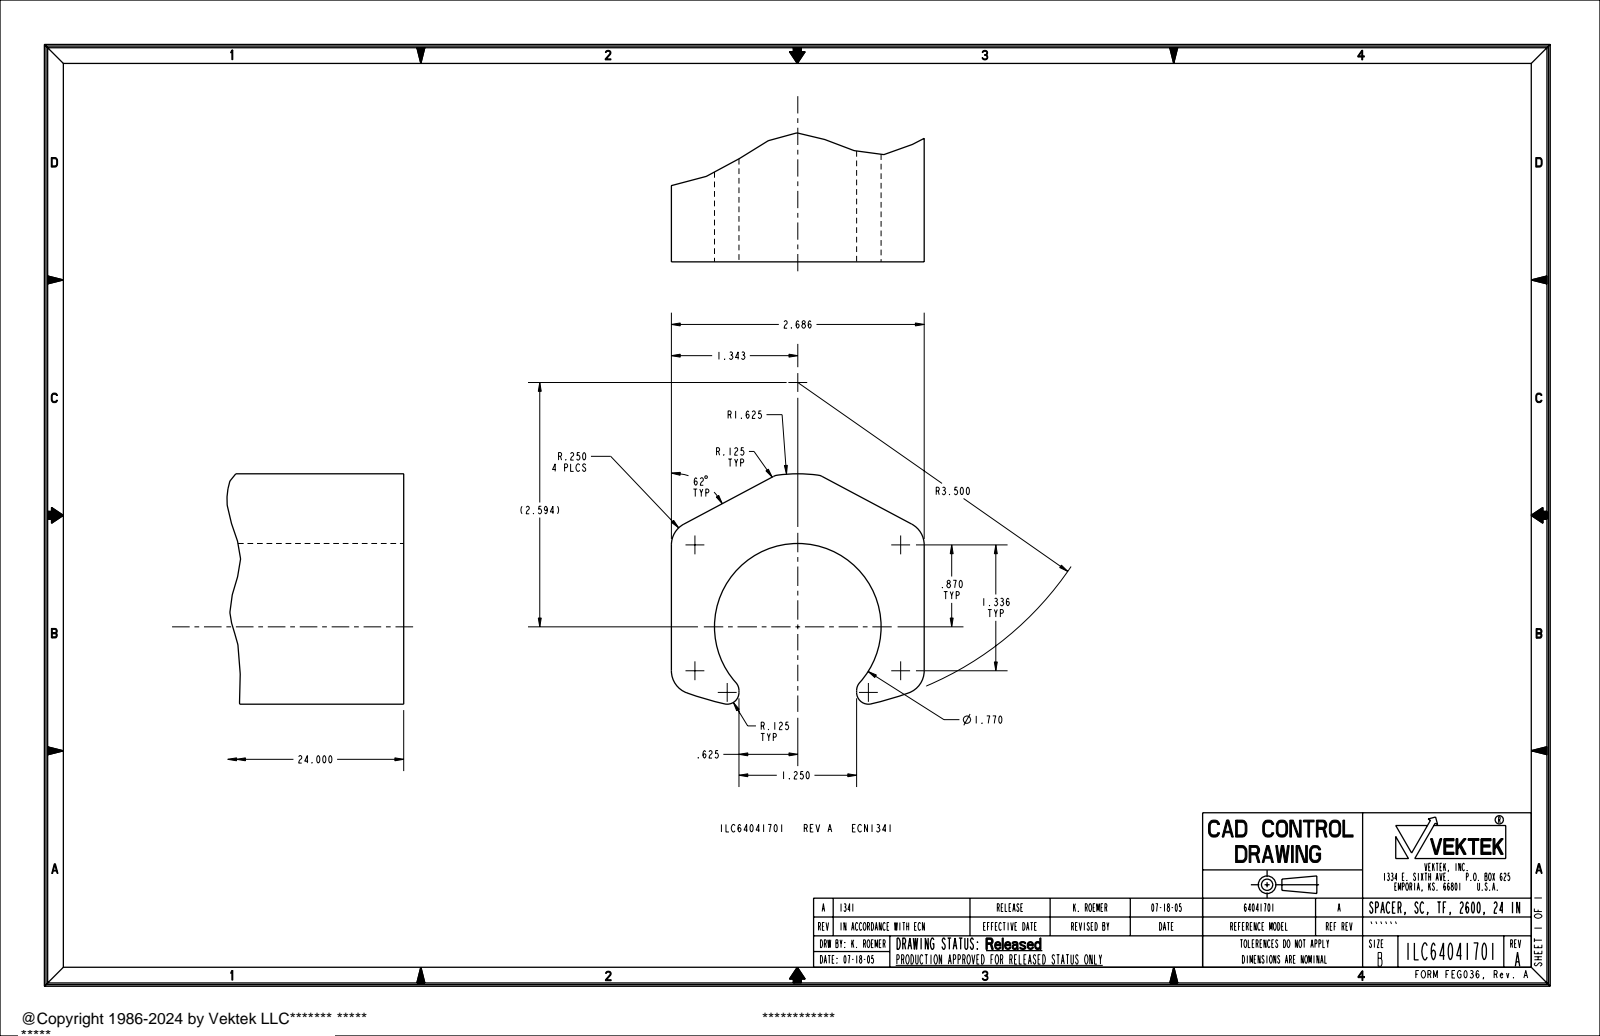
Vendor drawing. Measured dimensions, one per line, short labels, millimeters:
name: ILC64041701
written by: PRO/ENGINEER BY PARAMETRIC TECHNOLOGY CORPORATION, 2004290 (AUTOMOTIVE_DESIGN_CC2)
unit: mm
bodies: 1 solid, 22 faces (8 planar, 14 cylindrical, 0 other)
size: 609.6 × 68.2 × 62.1
volume: 1 289 000 mm³; area: 191 400 mm²
rounds: 6× R3.2, 4× R6.4, 1× R22.5, 1× R41.3, 1× R88.9
face distances: 68.2, 609.6, 18.2, 50, 31.8
